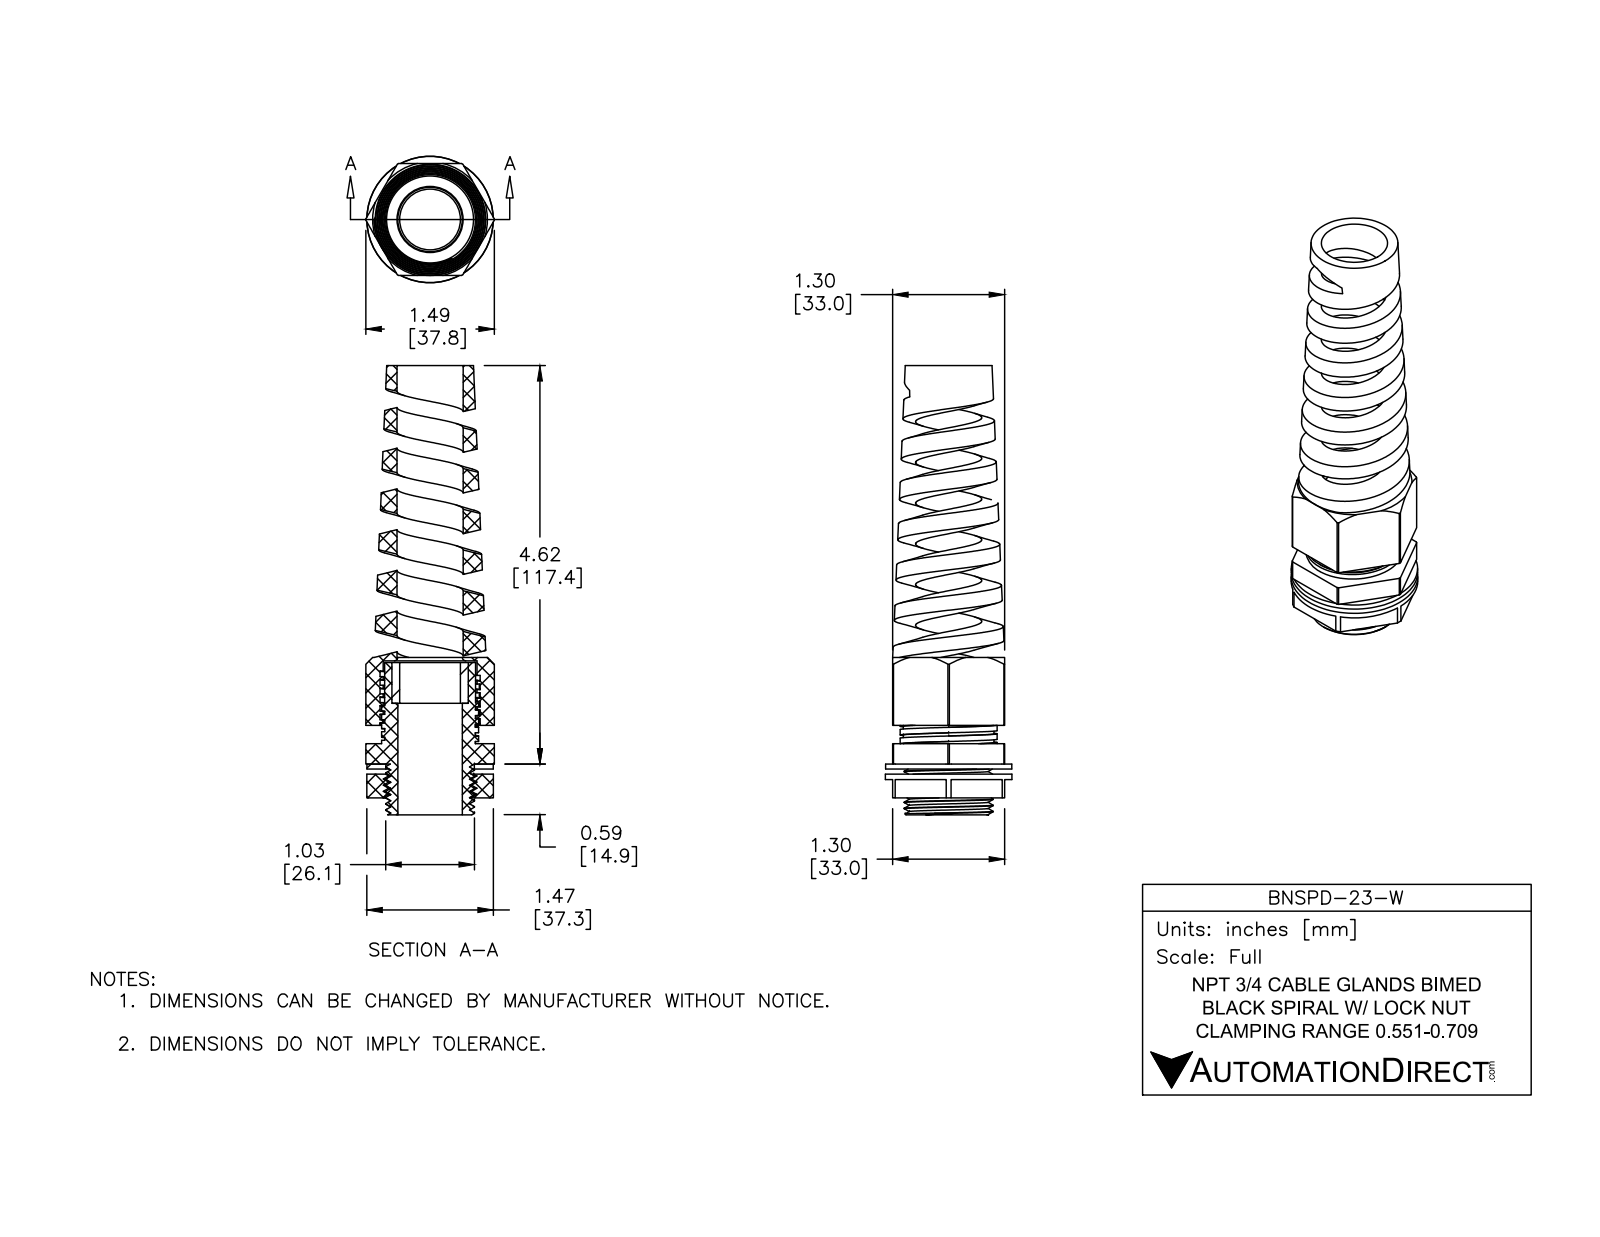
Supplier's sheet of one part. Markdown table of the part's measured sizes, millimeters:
| quantity | value |
| --- | --- |
| part name | BNSPDX-23-W |
| STEP written by | SolidWorks 2015 (CONFIG_CONTROL_DESIGN) |
| units | millimeters |
| bodies | 5 solids, 239 faces (105 planar, 97 cylindrical, 37 other) |
| overall size | 132.38 × 37.85 × 37.3 |
| volume | 41 174 mm³ |
| surface area | 35 147 mm² |
| round holes (diameter × count) | 17.9 × 1, 19 × 1, 19.5 × 1, 22.5 × 1, 24.69 × 1, 26.1 × 1, 27.67 × 1 |
| round bosses / shafts (diameter × count) | 37.3 × 1, 37.2 × 1, 28.6 × 1, 26.8 × 1, 26.14 × 1 |
| partial cylindrical surfaces (radius × count) | 18.92 × 1 |
| main face-to-face distances | 33, 1.5, 1, 31.4, 32.9, 2.5, 0.5, 15.5, 5.4, 7 |
